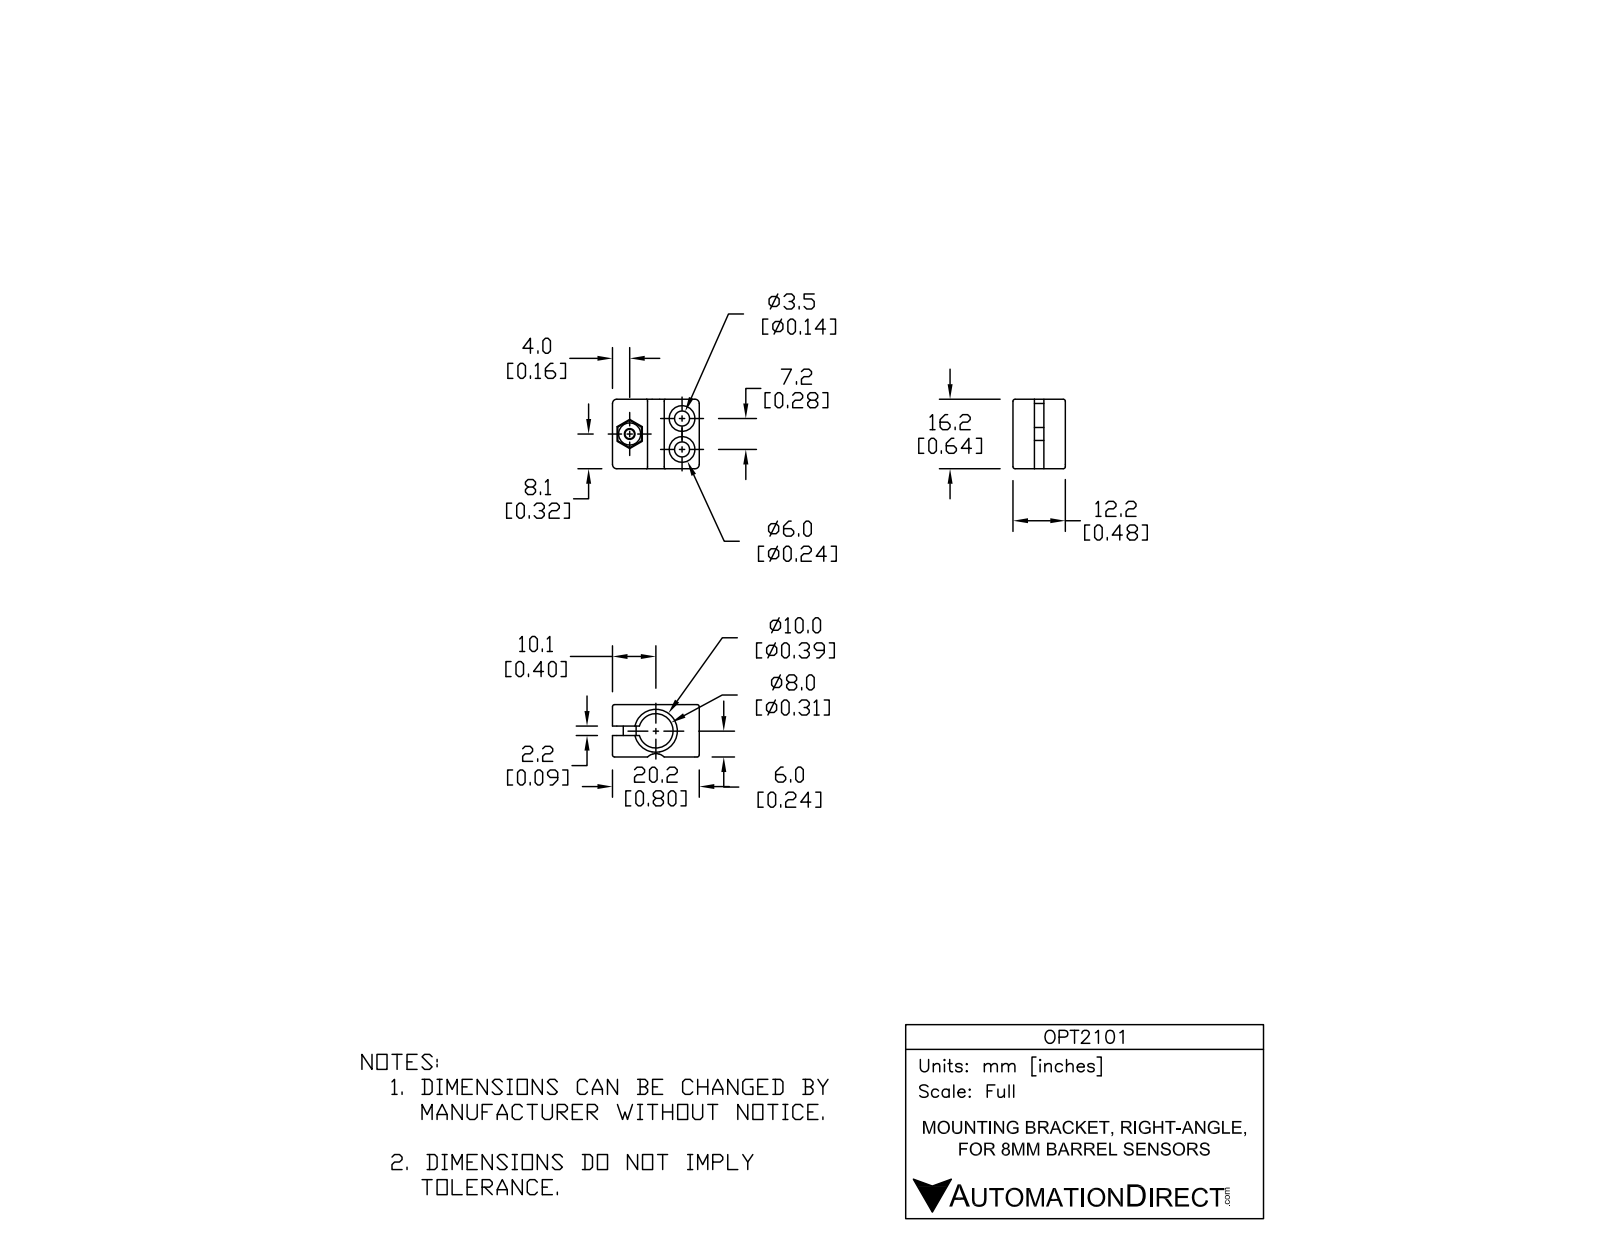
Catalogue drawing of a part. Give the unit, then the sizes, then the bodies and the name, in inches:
Units: inches
Overall size (bounding box): 0.795 × 0.638 × 0.48
Round holes (diameter × count): ⌀0.138 ×2, ⌀0.236 ×2, ⌀0.098 ×1, ⌀0.315 ×1
Round bosses / shafts (diameter × count): ⌀0.217 ×1, ⌀0.118 ×1
Partial cylindrical surfaces — rounded edges, fillets, slot ends (radius × count): R0.02 ×8, R0.039 ×4, R0.108 ×1
Main face-to-face distances: 0.283, 0.197, 0.48, 0.795, 0.638, 0.087, 0.231, 0.079, 0.118, 0.362
Hole centre spacings: 0.501, 0.283
Volume: 0.146 in³ · Surface area: 3.818 in²
Bodies: 1 solid, 88 faces (45 planar, 27 cylindrical, 16 other)
STEP written by: Unknown (CONFIG_CONTROL_DESIGN)
